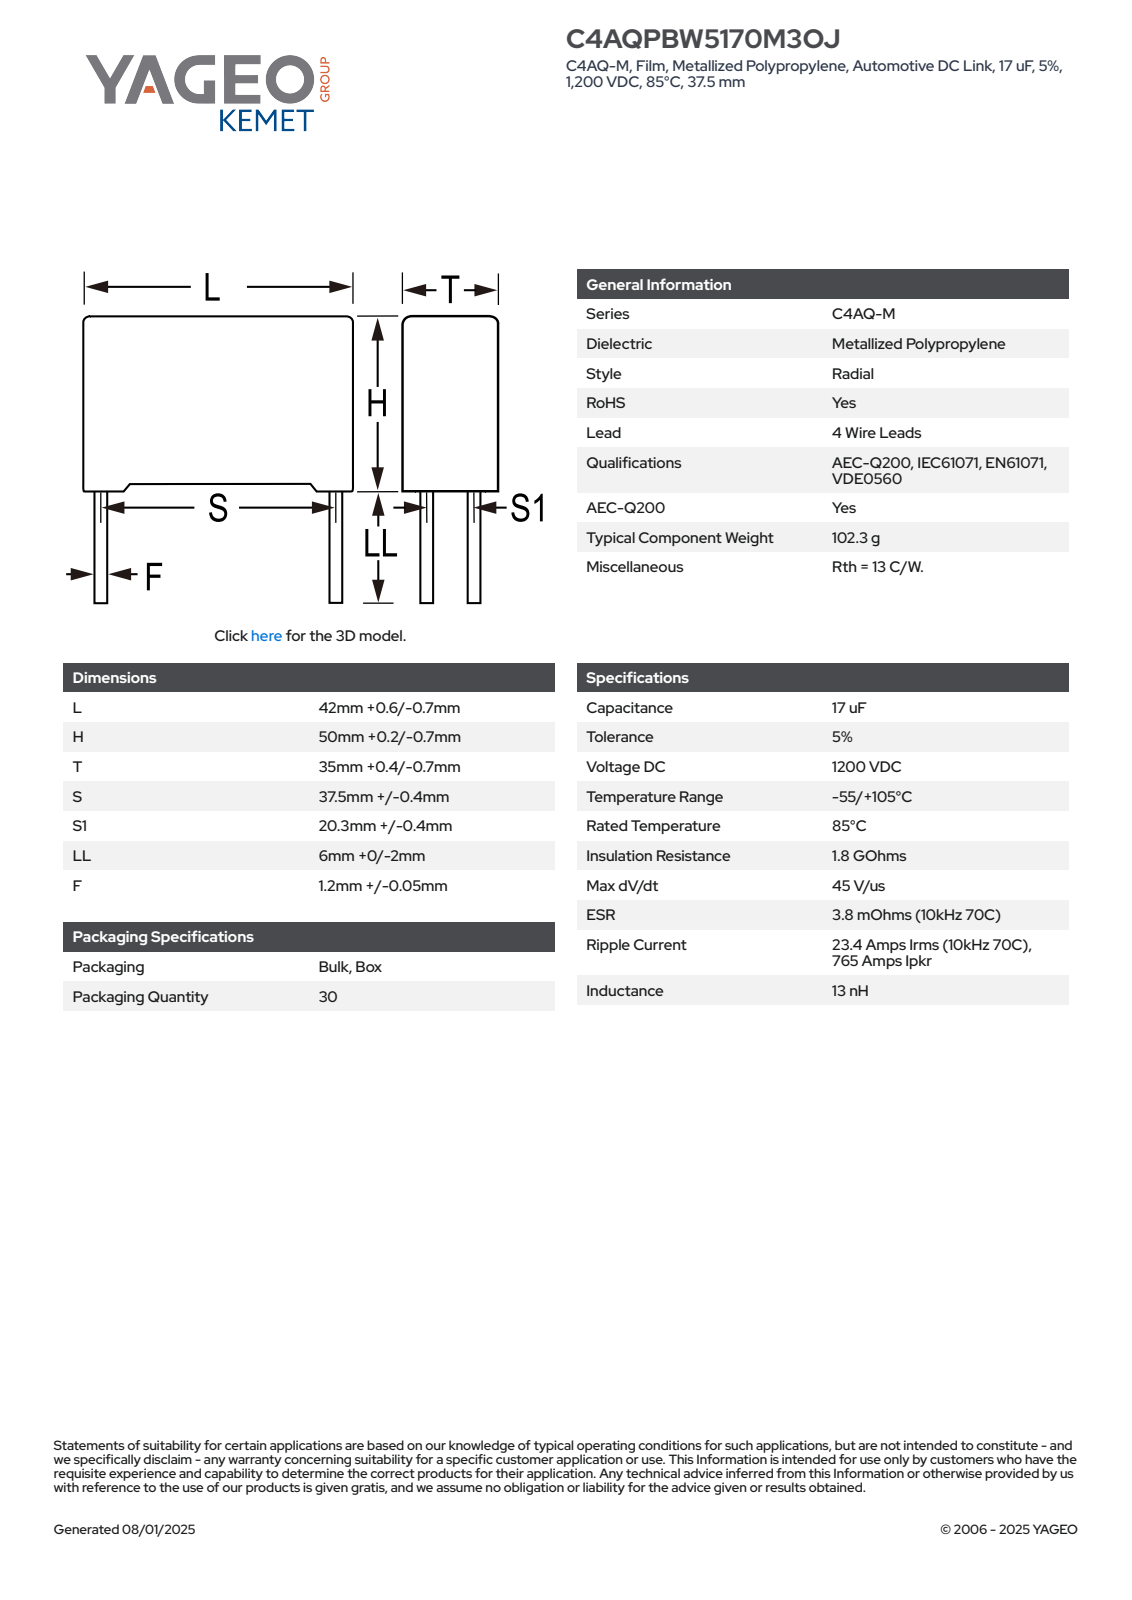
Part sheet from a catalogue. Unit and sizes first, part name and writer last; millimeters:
Units: millimetres
Overall size (bounding box): 56.2 × 42.6 × 35.41
Round bosses / shafts (diameter × count): ⌀1.25 ×4
Main face-to-face distances: 35.4, 42.6, 48.72, 1.48, 50.2, 2.18, 40.42, 35.41, 38.24, 33.22
Volume: 73 808 mm³ · Surface area: 11 117 mm²
Bodies: 4 solids, 91 faces (83 planar, 8 cylindrical, 0 other)
Part name (STEP PRODUCT): CFP_RB4_42X50X35_L42.6H50.2T35.4S37.5S120.3LL6F1.25
STEP written by: SolidWorks 2014 (AUTOMOTIVE_DESIGN)
